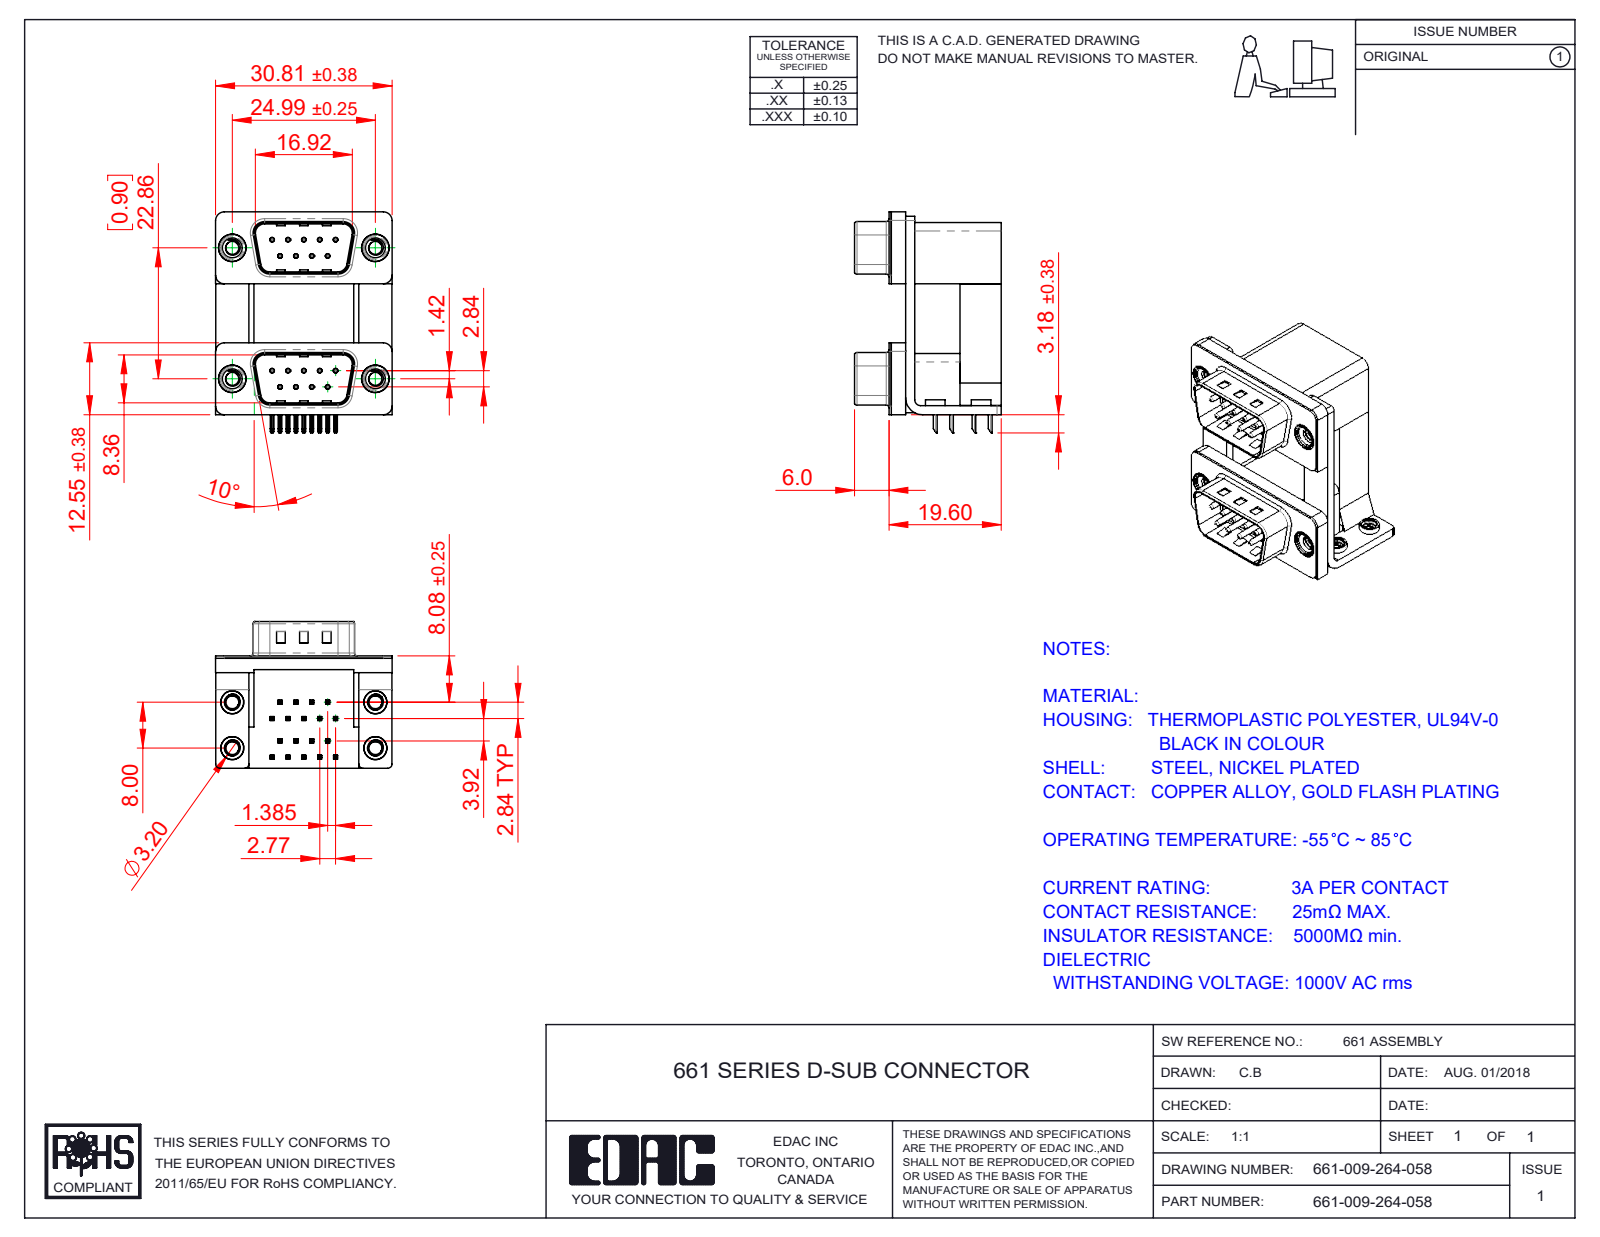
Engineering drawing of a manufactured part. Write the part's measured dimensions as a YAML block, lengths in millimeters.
part_name: "661 Contact Top Lower; 661 Housing Spacer_09 Contacts H; 661 Contact Bottom Upper_H; 661-009-264-058 (+8 more)"
step_written_by: "SolidWorks 2020 (CONFIG_CONTROL_DESIGN)"
units: millimeters
bodies: {solids: 33, faces: 2088, planar: 1164, cylindrical: 670, other: 254}
overall_size: [38.59, 30.81, 25.6]
volume: 10866
surface_area: 12584
round_holes:
  - {diameter: 0.35, count: 18}
  - {diameter: 0.8, count: 18}
  - {diameter: 2.26, count: 8}
  - {diameter: 2.75, count: 4}
  - {diameter: 3.2, count: 4}
  - {diameter: 3.5, count: 4}
  - {diameter: 4, count: 4}
  - {diameter: 4.8, count: 4}
  - {diameter: 5, count: 4}
round_bosses_or_shafts:
  - {diameter: 0.75, count: 18}
  - {diameter: 4.9, count: 4}
  - {diameter: 4.75, count: 4}
  - {diameter: 4, count: 4}
  - {diameter: 3.9, count: 4}
  - {diameter: 3.4, count: 4}
partial_cylinders:
  - {radius: 0.25, count: 72}
  - {radius: 0.12, count: 36}
  - {radius: 0.5, count: 16}
  - {radius: 1.5, count: 14}
  - {radius: 0.75, count: 8}
  - {radius: 0.9, count: 8}
  - {radius: 1.6, count: 8}
  - {radius: 2, count: 8}
face_to_face_distances: [0.4, 2.5, 22.86, 12, 16.7, 19.2, 7.2, 9.5, 12.4, 1.6]
hole_center_spacings: [3.16, 2.77, 23.03, 22.86, 5.54, 23.52, 20.07, 25.74]
